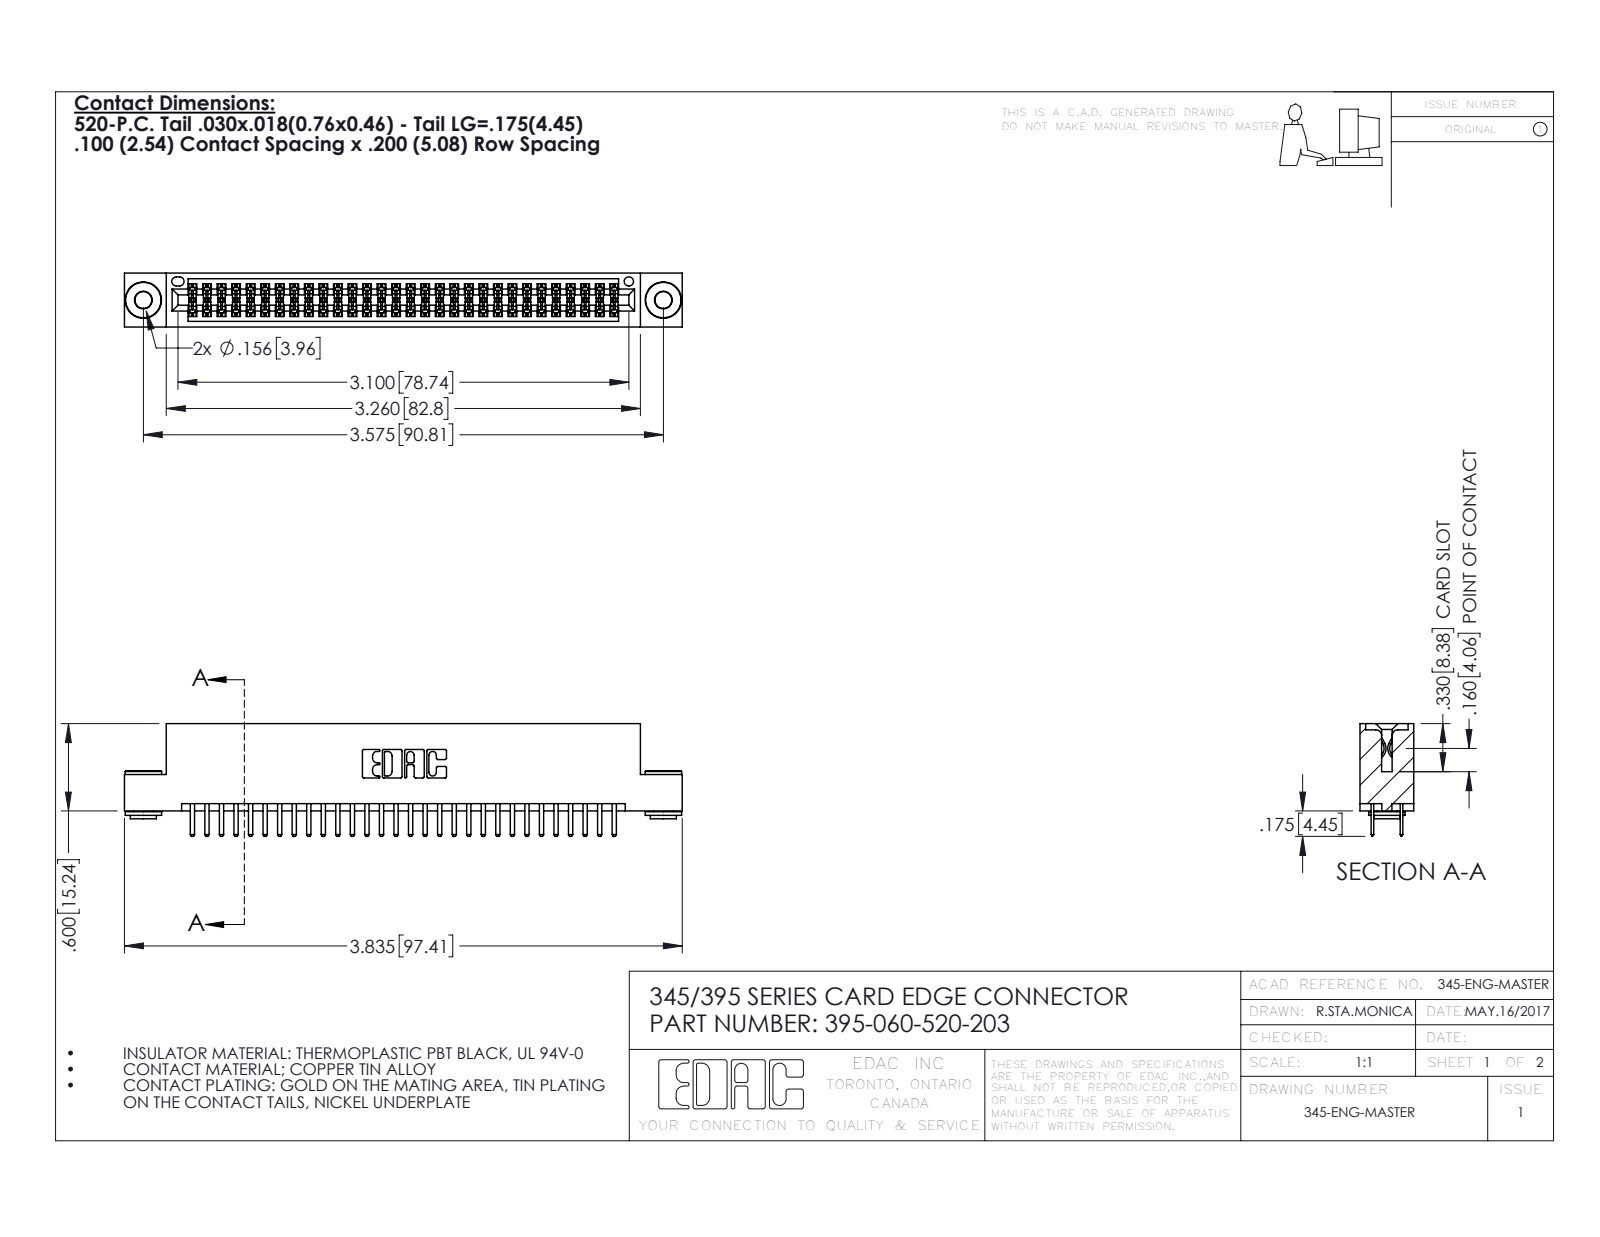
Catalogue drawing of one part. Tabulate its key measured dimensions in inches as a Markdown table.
| quantity | value |
| --- | --- |
| part name | 345 Part_Flush Mounting Lugs - 0.156 Dia-TH; 345-250-002_345-250-002-102; 345-292-001_345-293-120; 395-060-520-203 |
| STEP written by | SolidWorks 2016 (CONFIG_CONTROL_DESIGN) |
| units | inches |
| bodies | 63 solids, 3404 faces (2190 planar, 1206 cylindrical, 8 other) |
| overall size | 3.835 × 0.775 × 0.37 |
| volume | 0.57 in³ |
| surface area | 21.28 in² |
| round holes (diameter × count) | 0.116 × 2, 0.156 × 2, 0.064 × 1 |
| round bosses / shafts (diameter × count) | 0.25 × 2, 0.18 × 2, 0.136 × 2 |
| partial cylindrical surfaces (radius × count) | 0.006 × 90, 0.01 × 64, 0.01 × 22, 0.007 × 6, 0.031 × 6, 0.026 × 3, 0.014 × 2, 0.019 × 2 |
| main face-to-face distances | 0.072, 0.298, 0.2, 0.37, 0.025, 0.098, 0.272, 0.225, 0.022, 0.072 |
| hole center spacings | 0.27, 3.34, 3.575 |
